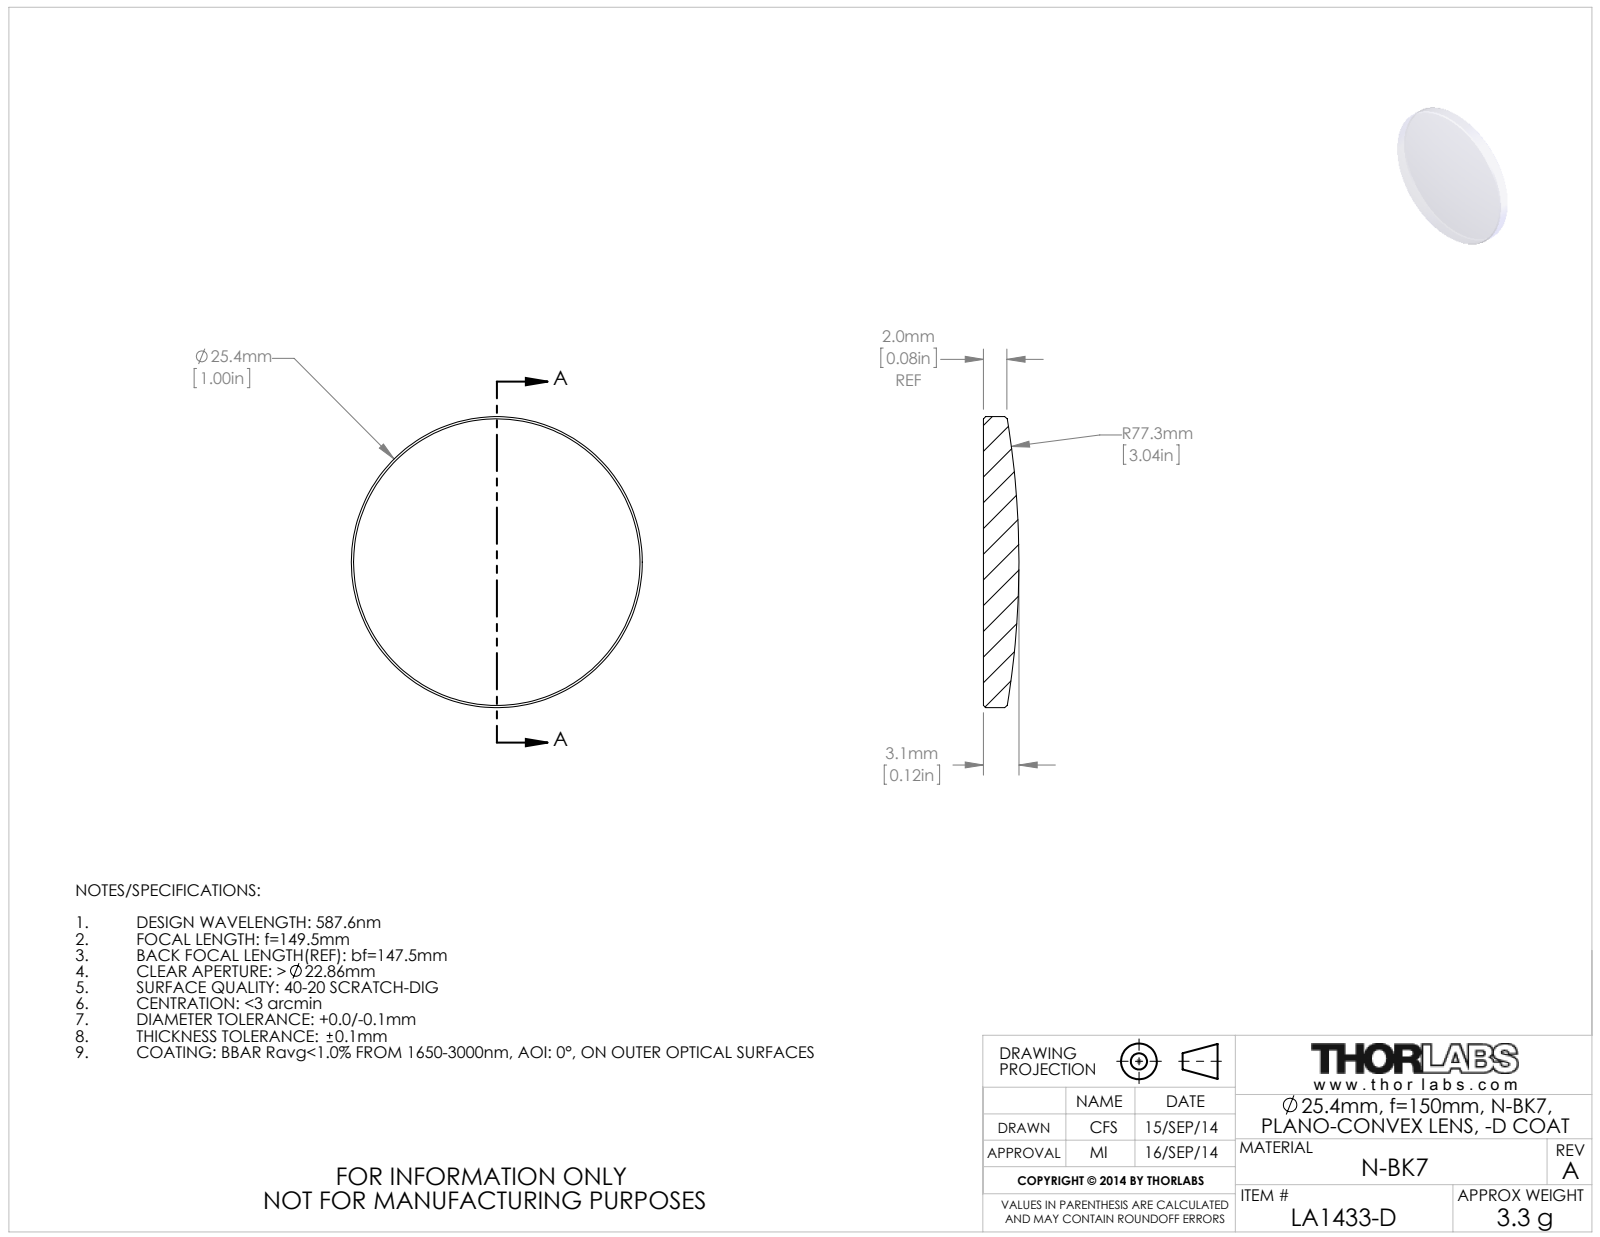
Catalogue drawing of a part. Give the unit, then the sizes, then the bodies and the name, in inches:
Units: inches
Overall size (bounding box): 1 × 1 × 0.122
Round bosses / shafts (diameter × count): ⌀1 ×1
Volume: 0.079 in³ · Surface area: 1.803 in²
Bodies: 1 solid, 9 faces (1 planar, 2 cylindrical, 6 other)
Part name (STEP PRODUCT): TTN031789-E0W
STEP written by: SolidWorks 2014 (CONFIG_CONTROL_DESIGN)
